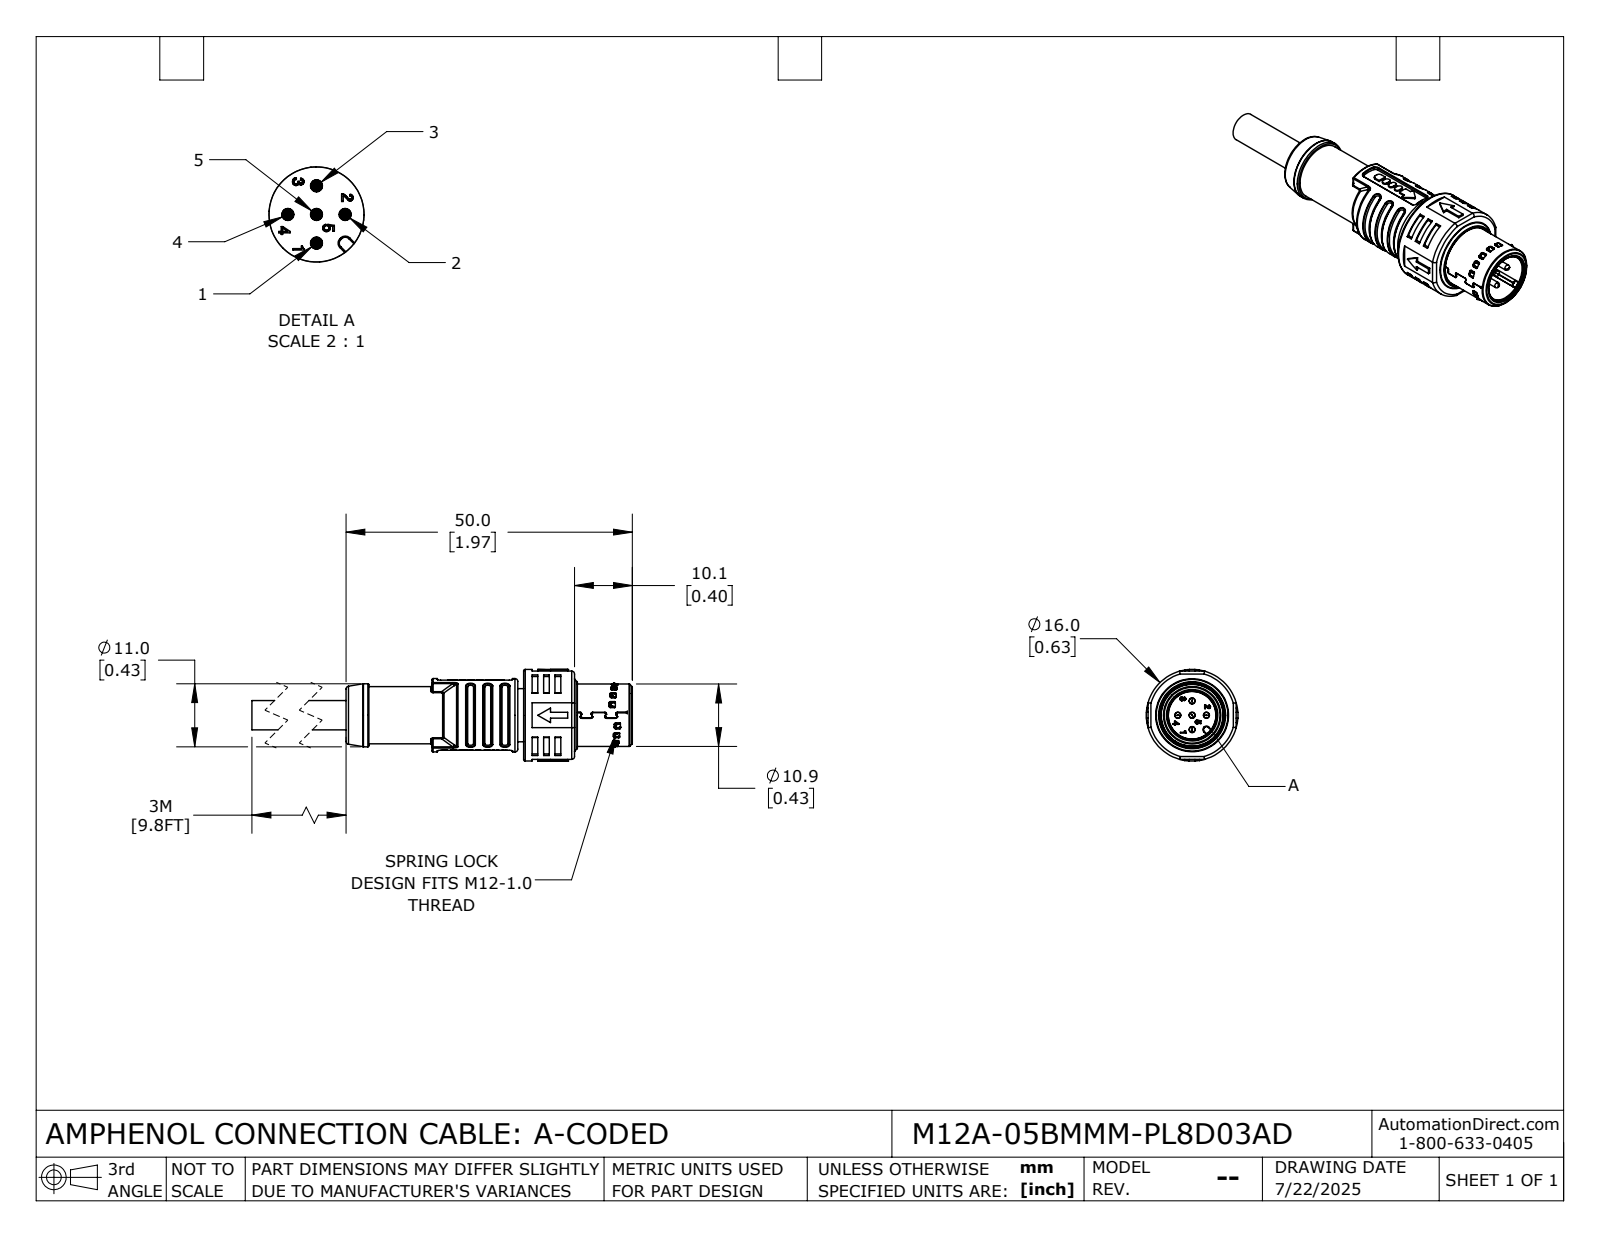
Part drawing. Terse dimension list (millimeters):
name: M12A-05BMMM-PL8D03AD
written by: SolidWorks 2024 (CONFIG_CONTROL_DESIGN)
unit: mm
bodies: 1 solid, 2230 faces (1085 planar, 648 cylindrical, 497 other)
size: 65 × 16 × 16
volume: 5 076 mm³; area: 5 586 mm²
holes: 5× ⌀1.05, 1× ⌀8.3, 1× ⌀9, 1× ⌀10.15, 1× ⌀10.5, 1× ⌀10.9, 1× ⌀11.5, 1× ⌀11.8, 1× ⌀14.2
bosses: 5× ⌀1, 1× ⌀16, 1× ⌀14.1, 1× ⌀12.8, 1× ⌀12.4, 1× ⌀11, 1× ⌀10.45, 1× ⌀10.4
rounds: 114× R0.2, 66× R0.25, 64× R0.3, 44× R0.15, 38× R0.5, 12× R0.13, 11× R0.7, 10× R0.1
face distances: 1, 10.1, 8.9, 8.6, 2.5, 30, 1.5, 1.2, 32.5, 15.4
hole spacings: 2.5, 3.54, 5
